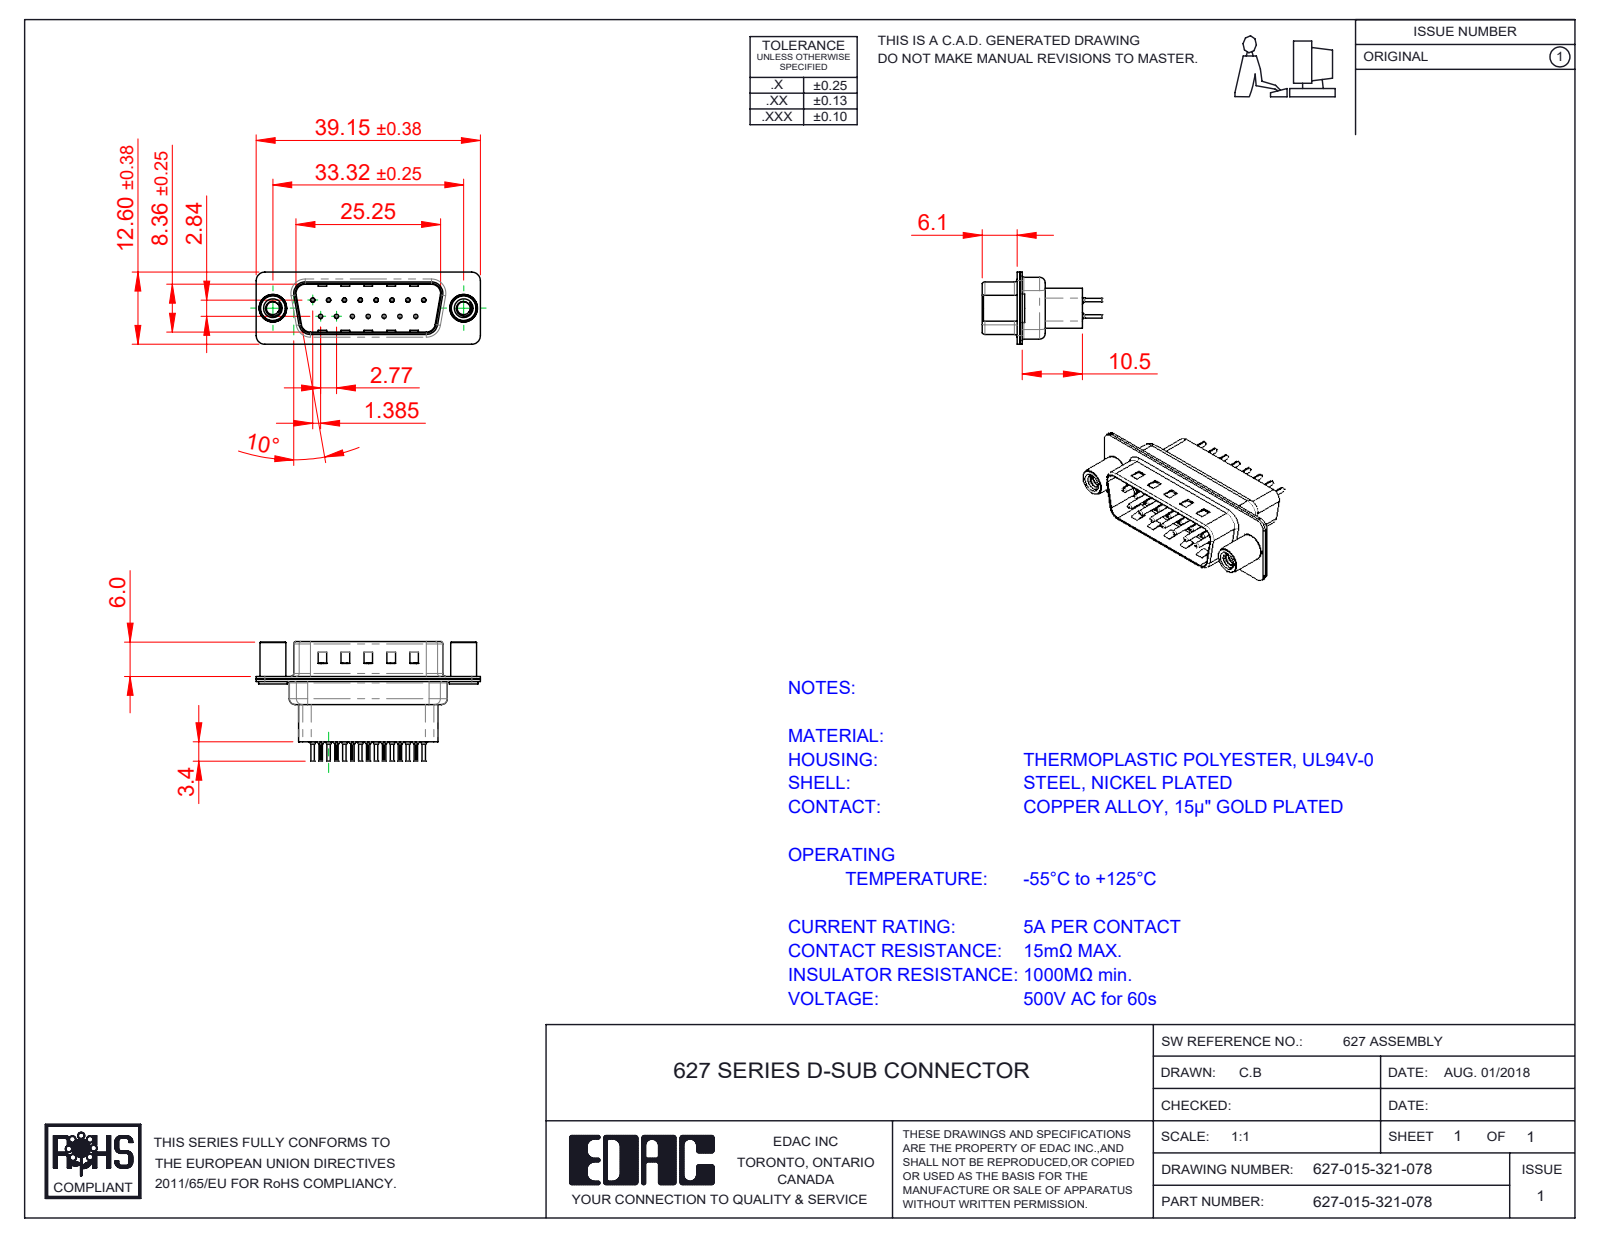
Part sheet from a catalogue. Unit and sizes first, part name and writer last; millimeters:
Units: millimetres
Overall size (bounding box): 39.15 × 20.8 × 12.6
Round holes (diameter × count): ⌀0.2 ×15, ⌀0.35 ×15, ⌀1.1 ×15, ⌀1.6 ×15, ⌀2.26 ×2, ⌀4 ×2, ⌀4.8 ×2
Round bosses / shafts (diameter × count): ⌀2 ×15, ⌀1.5 ×15, ⌀0.75 ×15, ⌀0.6 ×15, ⌀5 ×2, ⌀4.9 ×2, ⌀4.5 ×2
Partial cylindrical surfaces — rounded edges, fillets, slot ends (radius × count): R0.1 ×30, R1.5 ×16, R2 ×12, R0.5 ×8, R1.6 ×8, R0.25 ×4, R0.6 ×4, R0.65 ×4
Main face-to-face distances: 0.4, 0.45, 0.9, 0.82, 9.58, 1.5, 0.68, 7.68, 1.4, 1.08
Hole centre spacings: 3.16, 2.77, 5.54, 8.31, 11.08, 5.03, 5.04, 7.48
Volume: 2 602 mm³ · Surface area: 6 806 mm²
Bodies: 20 solids, 1844 faces (501 planar, 716 cylindrical, 627 other)
Part name (STEP PRODUCT): 627 Housing_15 HP; 627 Contact Row 2_21H; 627 Shell Front_15 Contacts; 627 Shell Rear_15 Contacts (+3 more)
STEP written by: SolidWorks 2020 (CONFIG_CONTROL_DESIGN)
